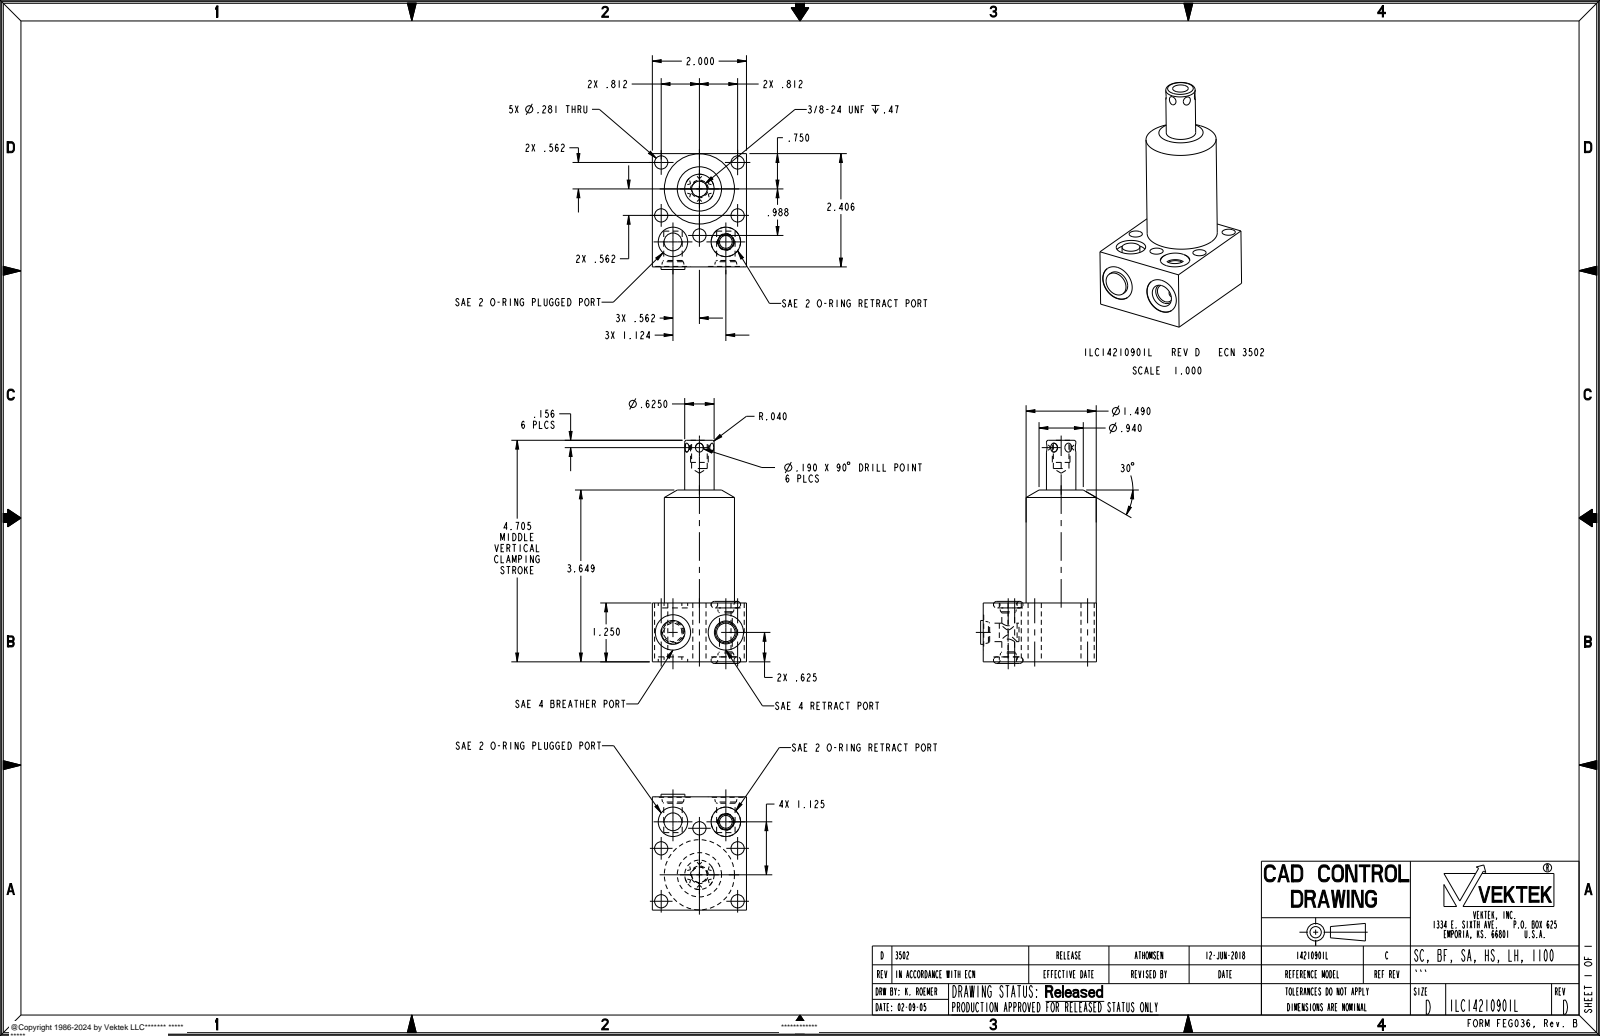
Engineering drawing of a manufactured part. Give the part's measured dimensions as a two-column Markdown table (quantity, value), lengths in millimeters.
| quantity | value |
| --- | --- |
| part name | ILC14210901L |
| STEP written by | PRO/ENGINEER BY PARAMETRIC TECHNOLOGY CORPORATION, 2013320 (AUTOMOTIVE_DESIGN) |
| units | millimeters |
| bodies | 3 solids, 109 faces (21 planar, 46 cylindrical, 42 other) |
| overall size | 120.4 × 62.5 × 50.8 |
| volume | 159 500 mm³ |
| surface area | 28 790 mm² |
| round holes (diameter × count) | 7.1 × 5, 10 × 2, 15.9 × 2, 19.1 × 2, 6.9 × 1, 8.4 × 1 |
| round bosses / shafts (diameter × count) | 37.8 × 1, 15.9 × 1, 12.9 × 1, 9.6 × 1, 9.5 × 1 |
| main face-to-face distances | 50.8, 31.8, 61.1, 2.7, 29.1, 60.9, 26.4, 92.7, 90, 63.6 |
| hole center spacings | 25.1, 28.5, 14.7, 15.6, 23.3, 31.9, 37.7, 41.2 |
